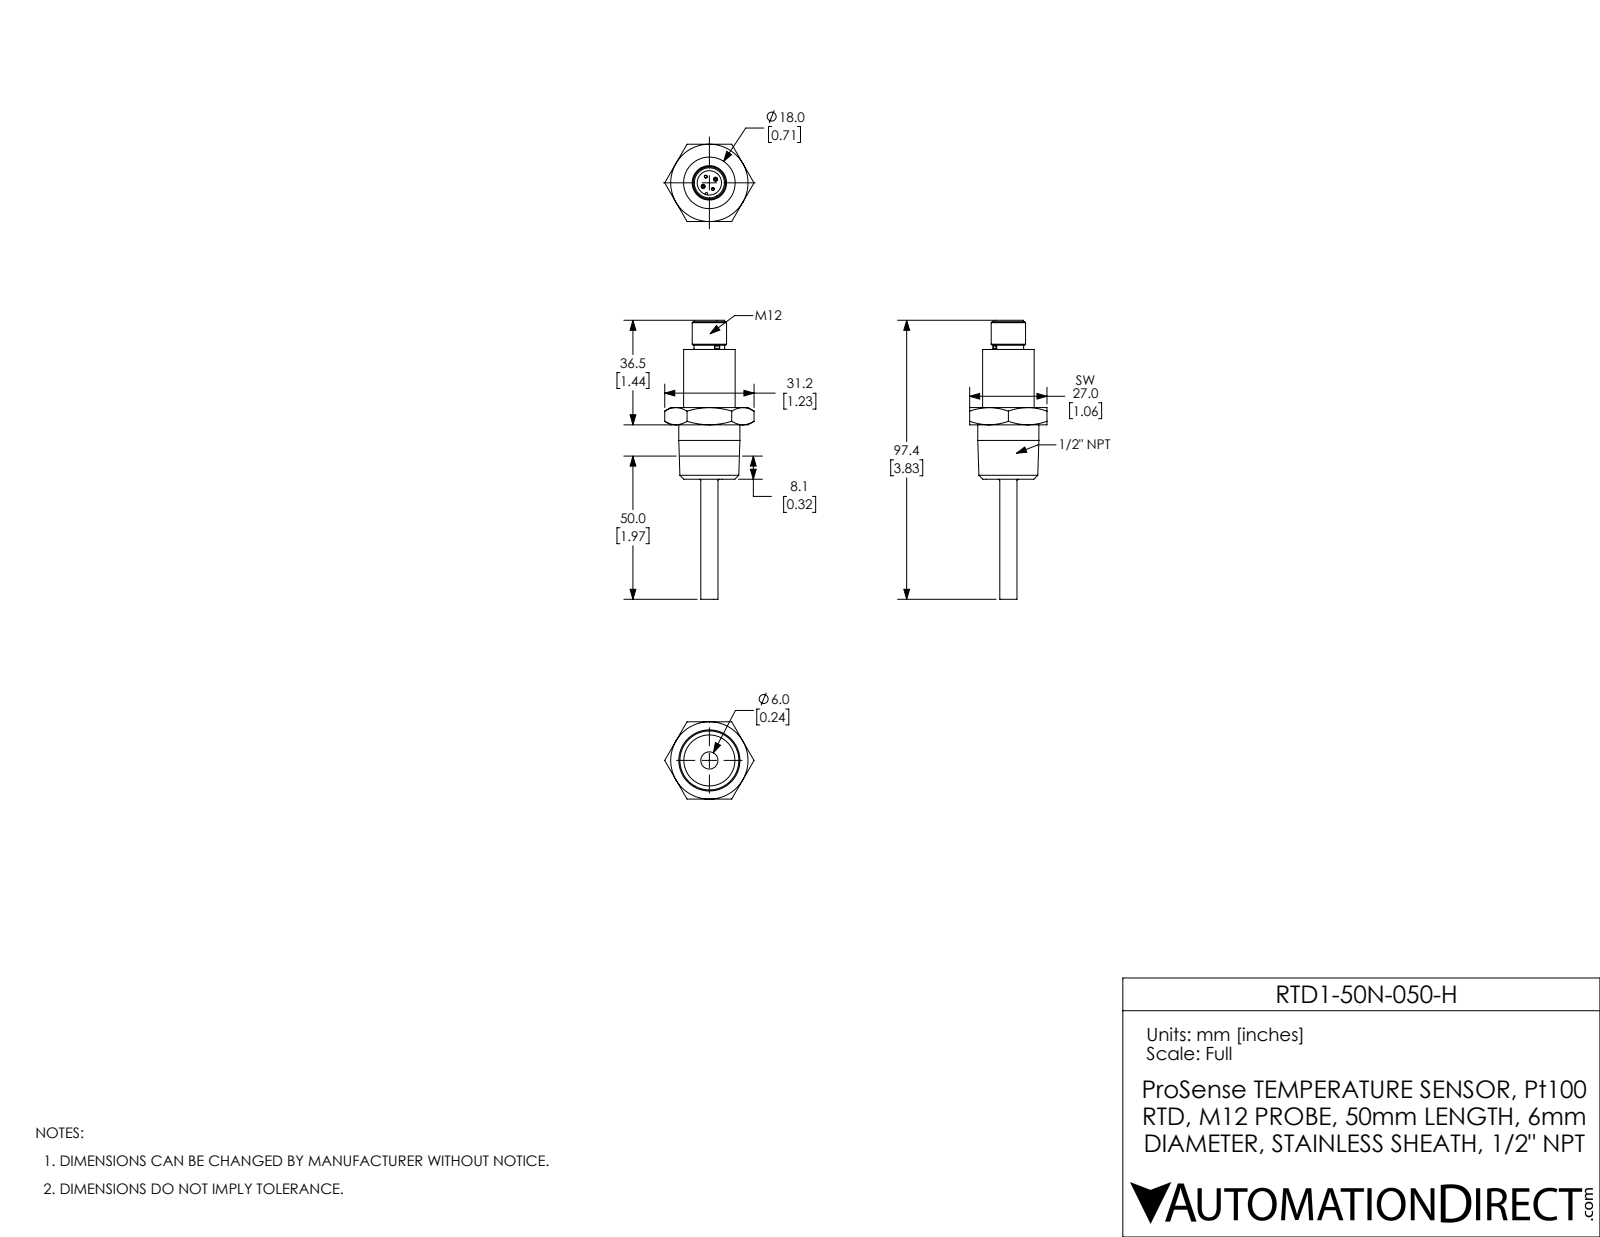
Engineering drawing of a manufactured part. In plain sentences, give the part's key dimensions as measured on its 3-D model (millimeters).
The part is named "RTD1-50N-050-H". Its 3-D file was written by "SolidWorks 2017 (AUTOMOTIVE_DESIGN)". It is 1 solid with 94 faces: 32 planar, 23 cylindrical and 39 other. Overall it measures 97.4 by 31.2 by 27 millimeters. Its volume is 17 260 cubic millimeters and its surface area 5 577 square millimeters. Round holes: 1 of diameter 8.5. Round bosses or shafts: 4 of diameter 1, 1 of diameter 21.3, 1 of diameter 18, 1 of diameter 12, 1 of diameter 10.7, 1 of diameter 10.5, 1 of diameter 6. Partial cylindrical surfaces (rounded edges, fillets, slot ends): 1 of radius 0.4. The main face-to-face distances are 27, 6, 19, 25, 45.3, 26.3, 20.3, 46.5, 27.5, 21.5.
